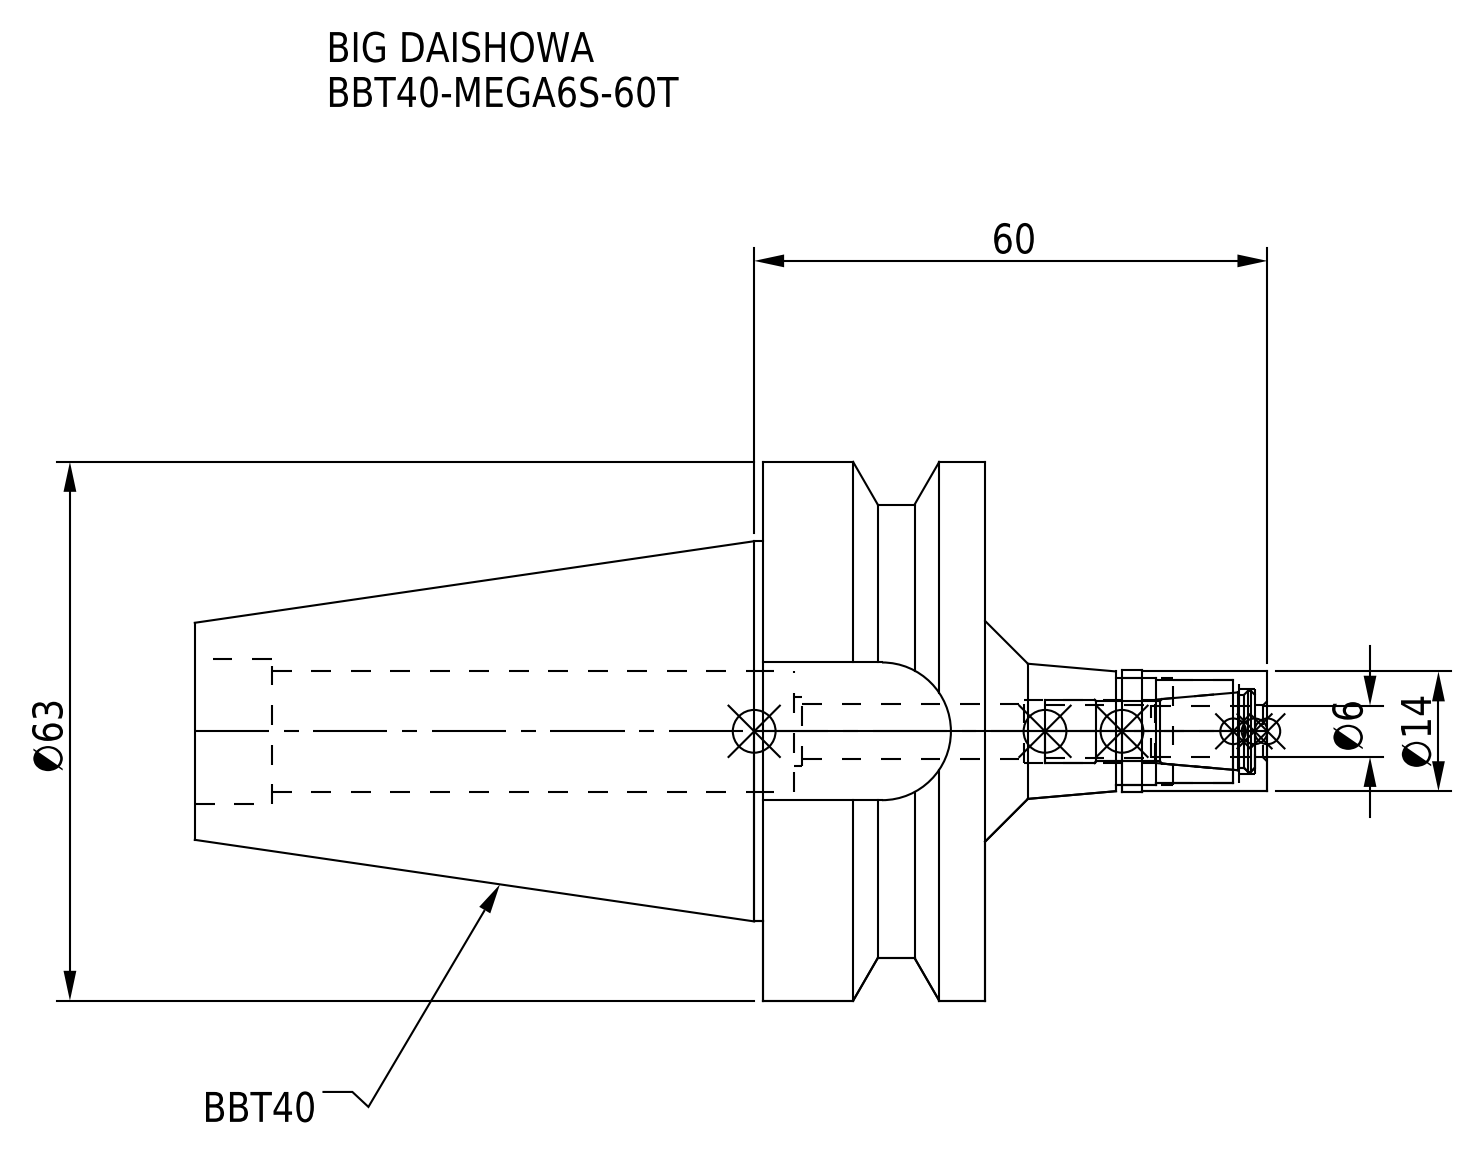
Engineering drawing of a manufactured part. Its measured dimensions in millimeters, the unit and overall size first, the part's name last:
Units: millimetres
Overall size (bounding box): 125.4 × 63 × 63
Round holes (diameter × count): ⌀6.1 ×1, ⌀6.4 ×1, ⌀7.4 ×1, ⌀8 ×1, ⌀10 ×1, ⌀12 ×1, ⌀12.5 ×1, ⌀14.2 ×1, ⌀17 ×1
Round bosses / shafts (diameter × count): ⌀63 ×1, ⌀53 ×1, ⌀44.45 ×1, ⌀14.3 ×1, ⌀14 ×1
Partial cylindrical surfaces — rounded edges, fillets, slot ends (radius × count): R8.05 ×1
Main face-to-face distances: 26, 45, 92.4, 66.4, 16.1, 33, 59, 125.4, 55.4, 22.4
Volume: 127 810 mm³ · Surface area: 25 788 mm²
Bodies: 2 solids, 74 faces (22 planar, 38 cylindrical, 14 other)
Part name (STEP PRODUCT): BBT40MS06060T-060_ASM.stp; DXF_TEMP_ASSY_ASM_4_ASM.stp; BBT40-MEGA6S-60T_1.stp; BBT40-MEGA6S-60T (+3 more)
STEP written by: SolidWorks 2019 (CONFIG_CONTROL_DESIGN)
